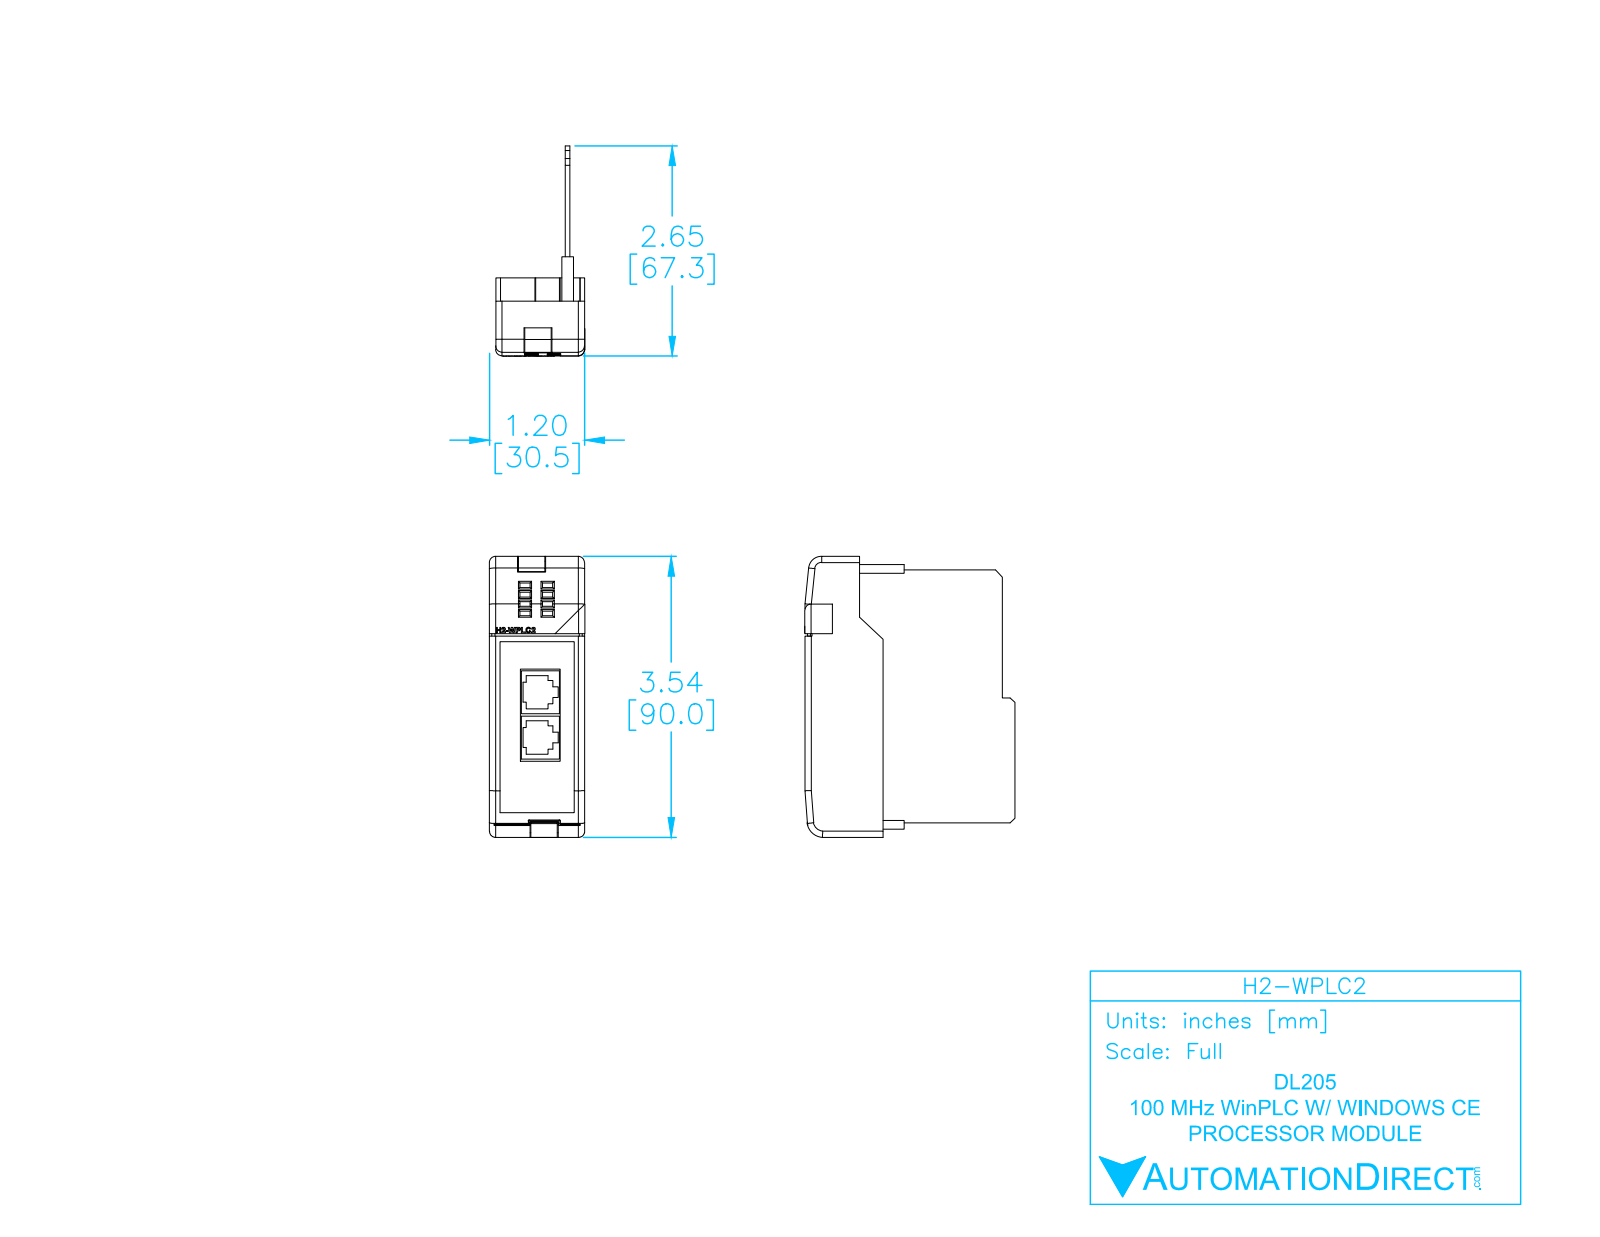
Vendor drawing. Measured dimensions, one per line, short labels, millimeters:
name: H2-WPLC2
written by: SolidWorks 2009 (AUTOMOTIVE_DESIGN)
unit: mm
bodies: 4 solids, 408 faces (281 planar, 84 cylindrical, 43 other)
size: 90 × 67.38 × 30.55
volume: 19 329 mm³; area: 29 785 mm²
rounds: 28× R0.5, 11× R2, 4× R0.25, 2× R1, 1× R2.62, 1× R3.79, 1× R4.12, 1× R5.29
face distances: 1.5, 4.72, 3.22, 6.22, 24.28, 29, 0.5, 25.78, 30.5, 22.78
